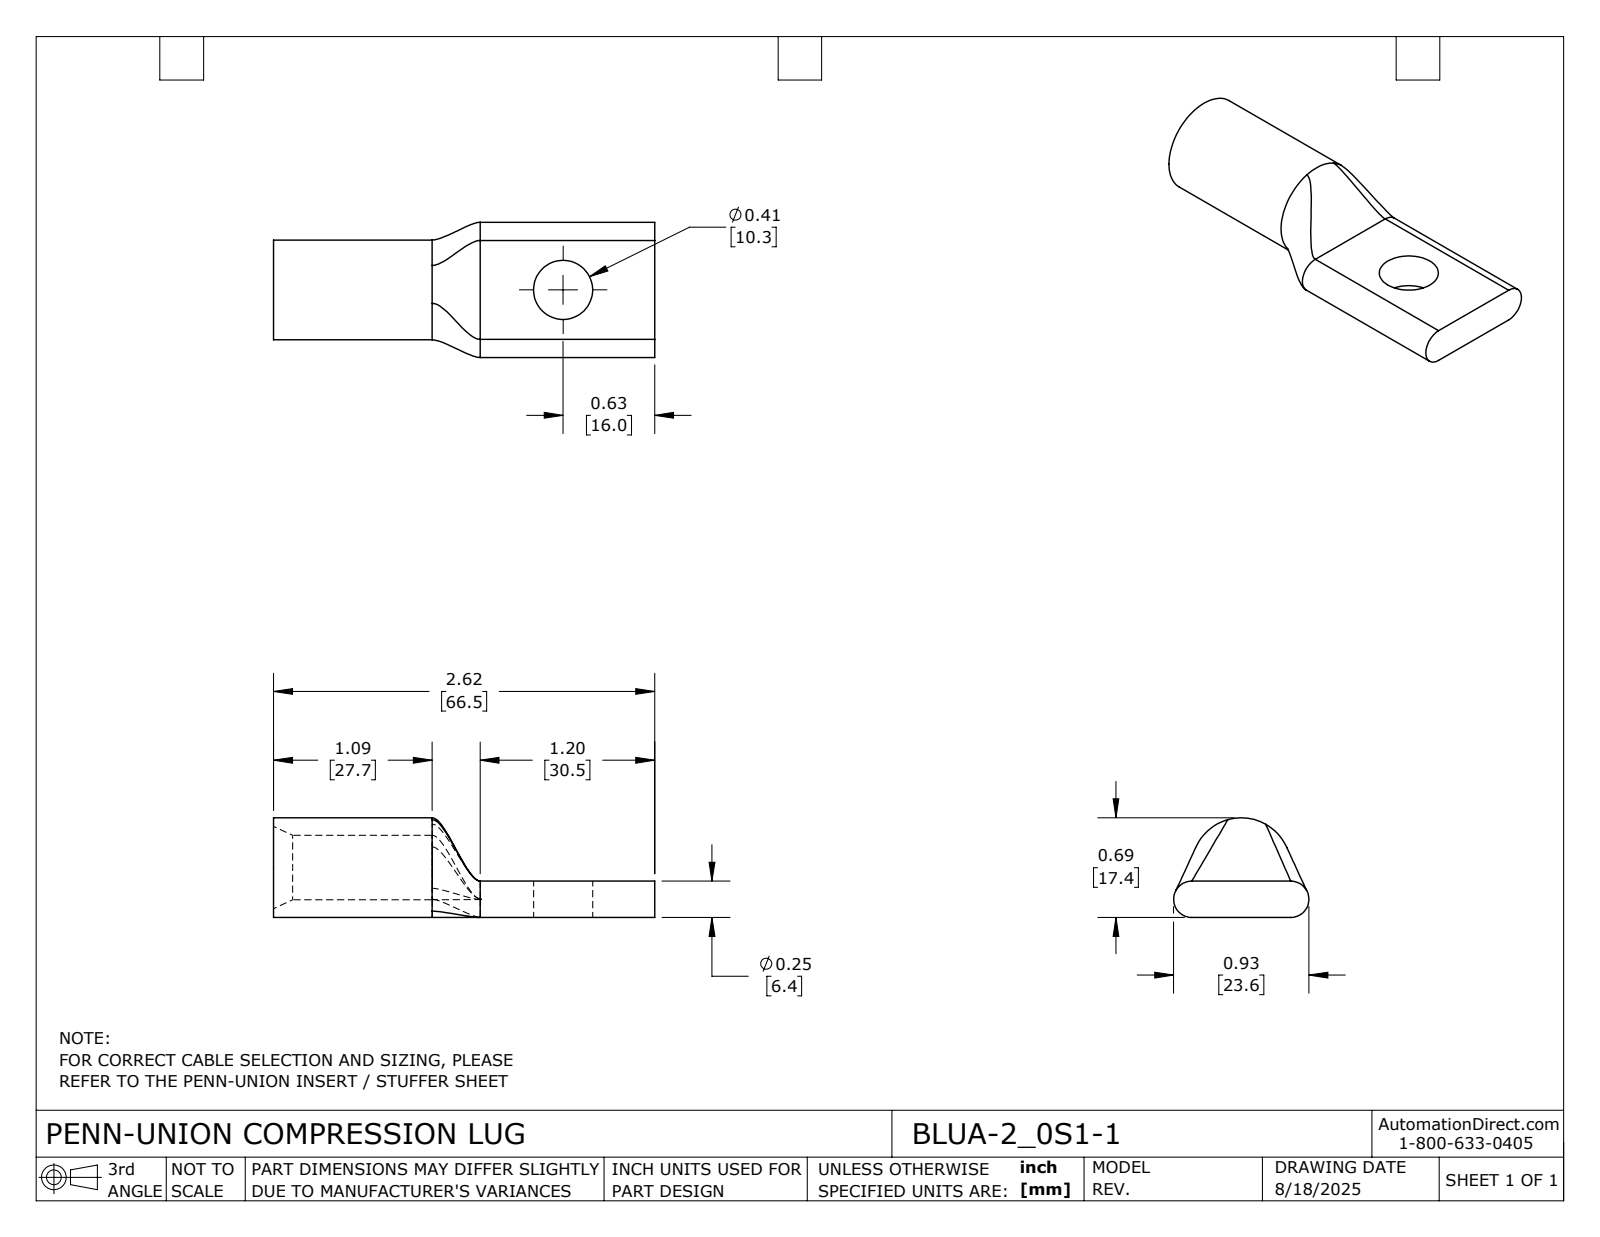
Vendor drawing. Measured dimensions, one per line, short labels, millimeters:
name: BLUA-2_0S1-1
written by: SolidWorks 2024 (CONFIG_CONTROL_DESIGN)
unit: mm
bodies: 1 solid, 24 faces (5 planar, 9 cylindrical, 10 other)
size: 66.5 × 23.6 × 17.4
volume: 8 670 mm³; area: 5 352 mm²
holes: 1× ⌀10.3, 1× ⌀11.3
bosses: 1× ⌀17.4
rounds: 2× R3.2
face distances: 6.4, 66.5, 36.1, 30.5
